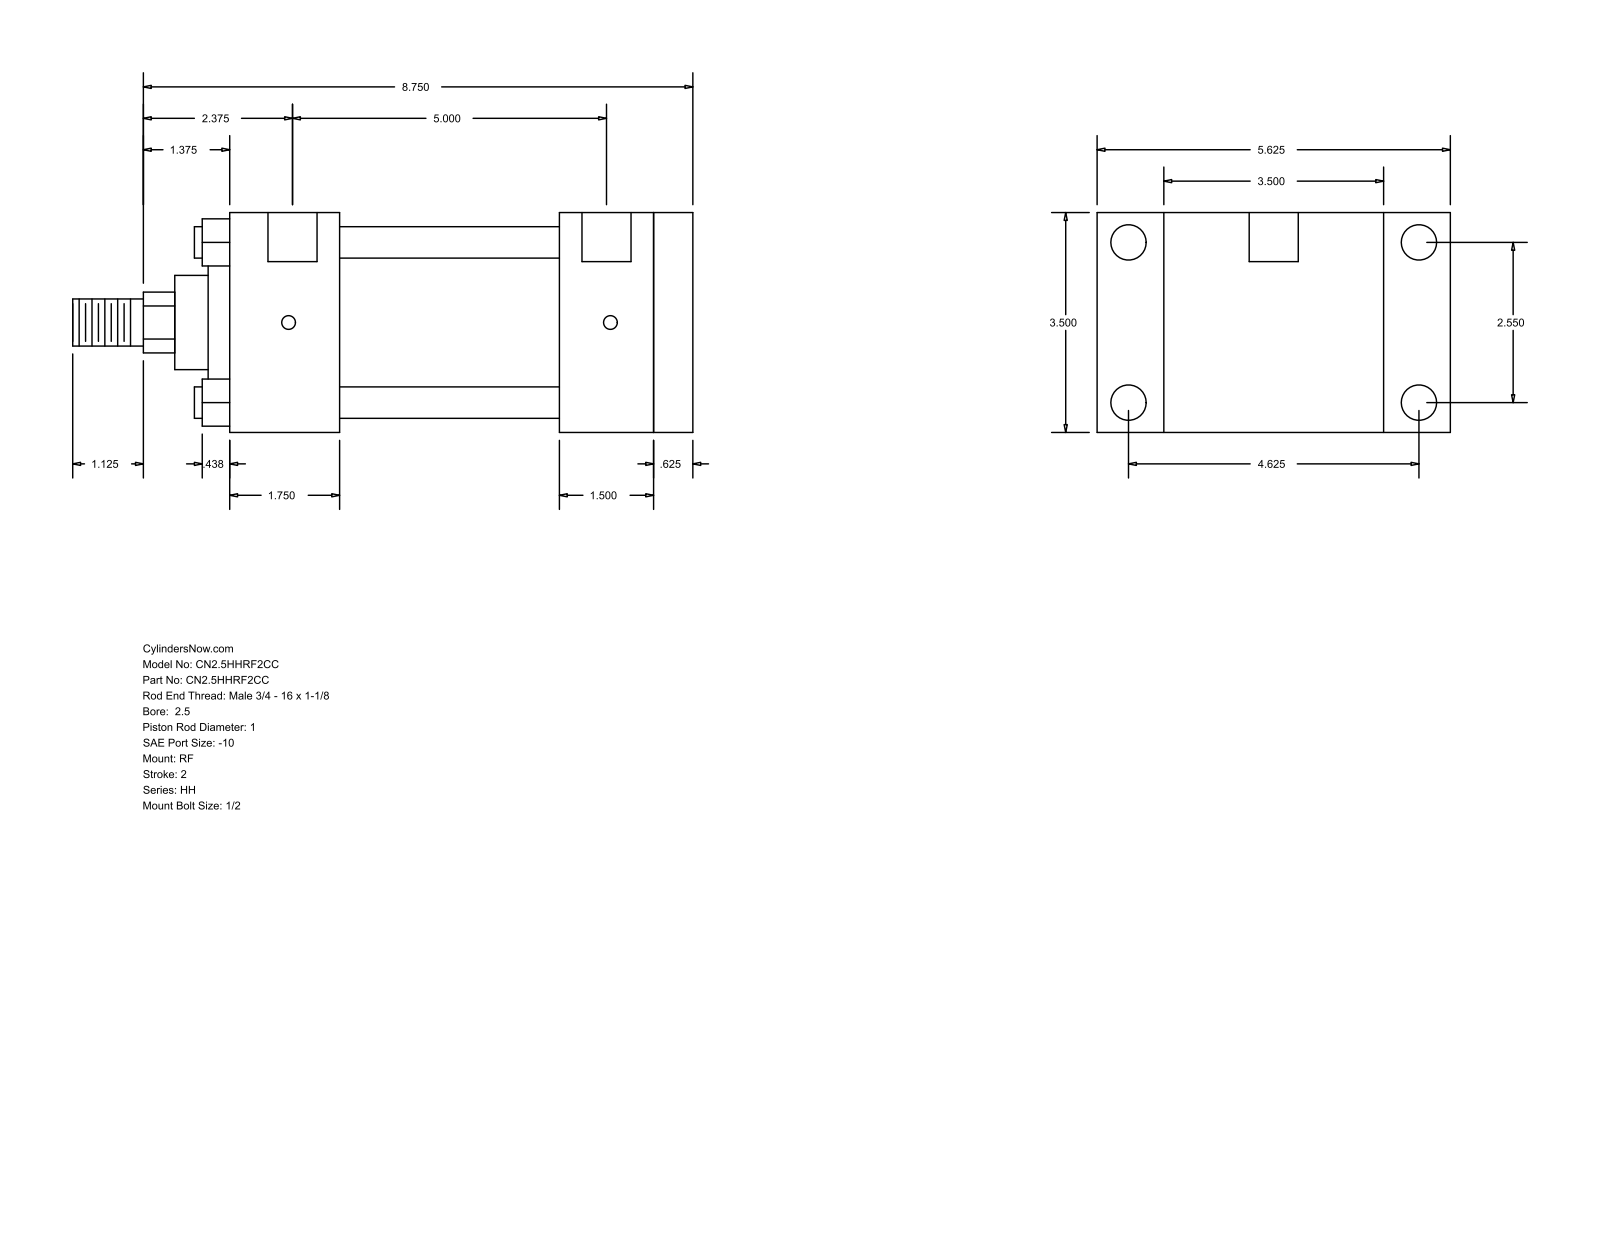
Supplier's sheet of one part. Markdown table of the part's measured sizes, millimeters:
| quantity | value |
| --- | --- |
| part name | HH_RF__0250_1 |
| STEP written by | GSSL Pune (CONFIG_CONTROL_DESIGN) |
| units | millimeters |
| bodies | 0 solids, 94 faces (65 planar, 29 cylindrical, 0 other) |
| overall size | 250.82 × 142.88 × 88.9 |
| round holes (diameter × count) | 5.56 × 4, 14.3 × 4, 19.84 × 2 |
| round bosses / shafts (diameter × count) | 12.7 × 4, 73.03 × 1, 60.33 × 1, 38.1 × 1, 25.4 × 1, 19.05 × 1 |
| partial cylindrical surfaces (radius × count) | 12.29 × 1 |
| main face-to-face distances | 88.9, 15.87, 171.46, 187.33, 38.1, 44.46, 127, 142.87, 133.36, 53.97 |
| hole center spacings | 1.59, 64.76, 117.48, 128.58, 130.17, 134.15, 126.99 |
